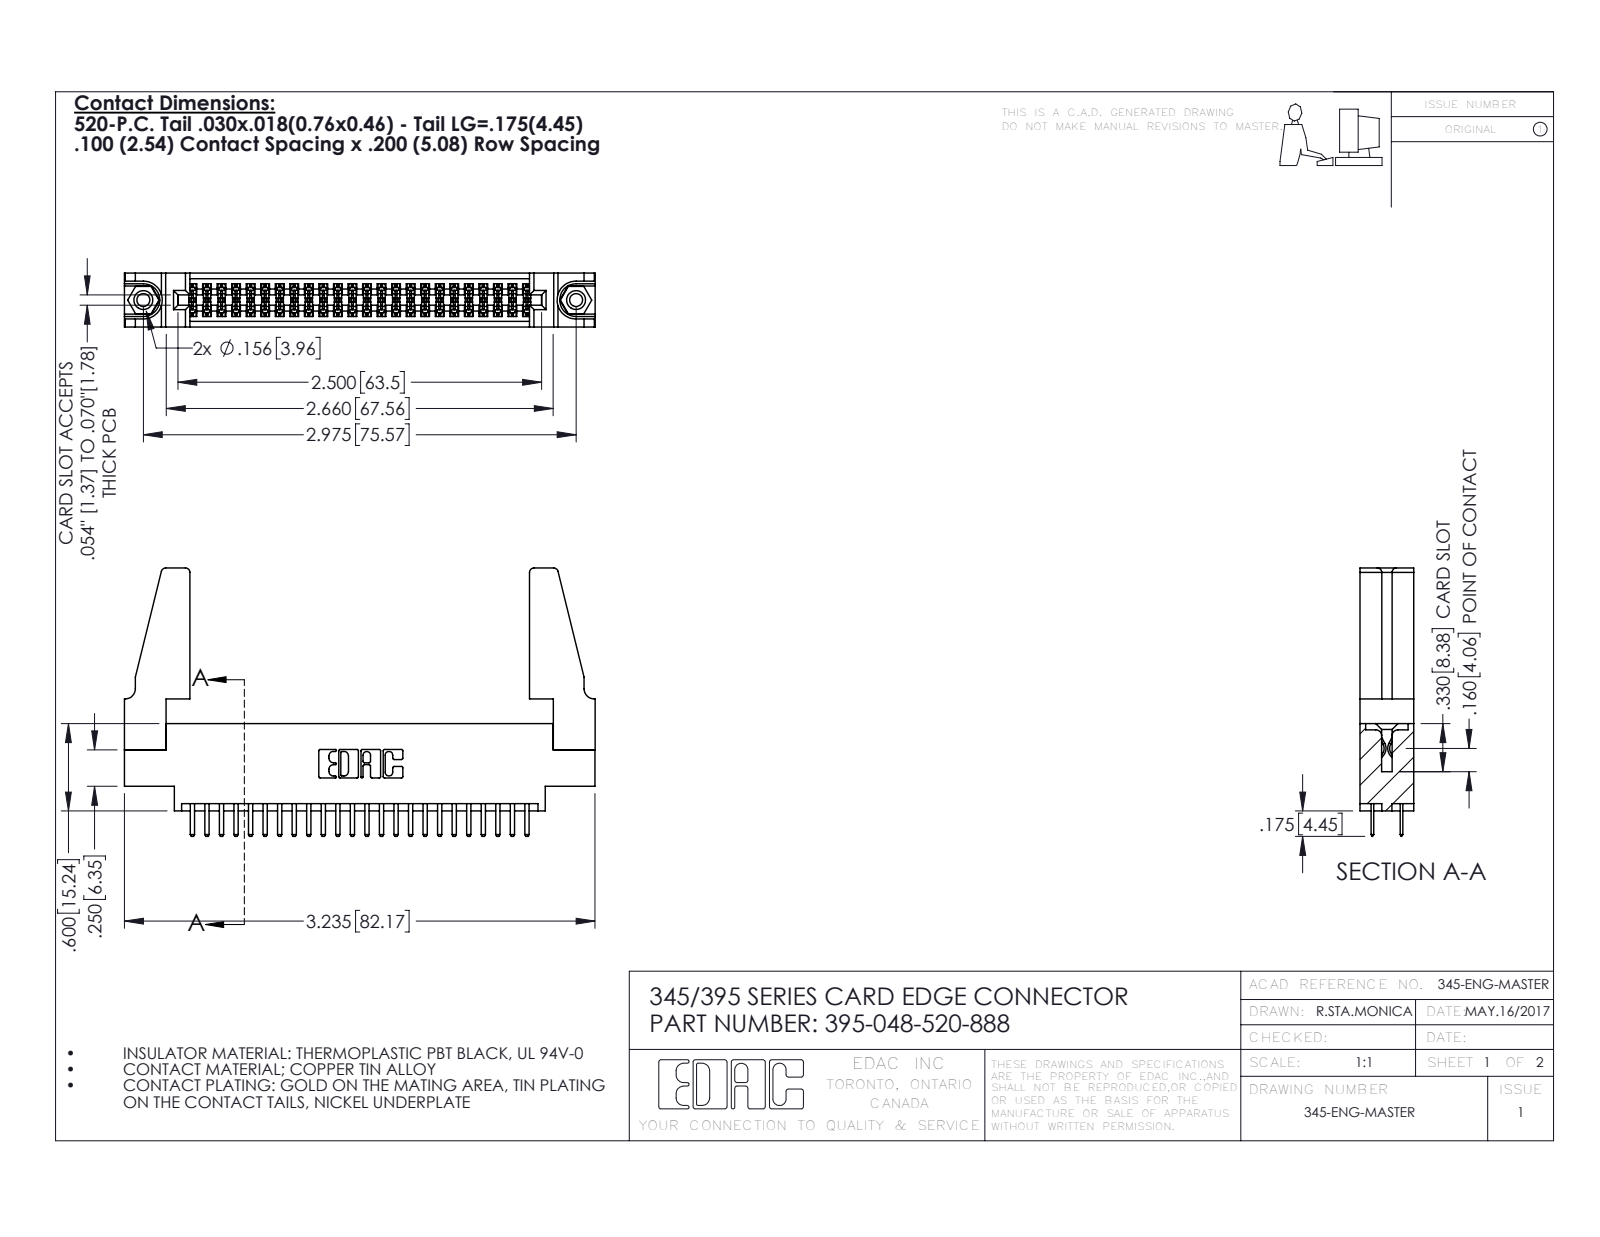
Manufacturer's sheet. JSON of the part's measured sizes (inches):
{"part_name": "345 Part_0.170 Offset - 0.156 Dia-TH; 395-048-520-888; 345-220-078_345-220-088; 345-250-001_345-250-001-102 (+1 more)", "step_written_by": "SolidWorks 2016 (CONFIG_CONTROL_DESIGN)", "units": "inches", "bodies": {"solids": 53, "faces": 2846, "planar": 1836, "cylindrical": 994, "other": 16}, "overall_size": [3.236, 1.845, 0.37], "volume_in3": 0.667, "surface_area_in2": 22.05, "round_holes": [[0.089, 2], [0.125, 2], [0.156, 2], [0.064, 1]], "round_bosses_or_shafts": [[0.155, 2]], "partial_cylinders_radius": [[0.006, 72], [0.01, 52], [0.01, 22], [0.03, 8], [0.007, 6], [0.031, 6], [0.026, 3], [0.014, 2]], "face_to_face_distances": [0.37, 0.072, 0.298, 0.2, 0.098, 0.272, 0.025, 0.225, 0.022, 0.175], "hole_center_spacings": [0.27, 2.741, 2.975]}
